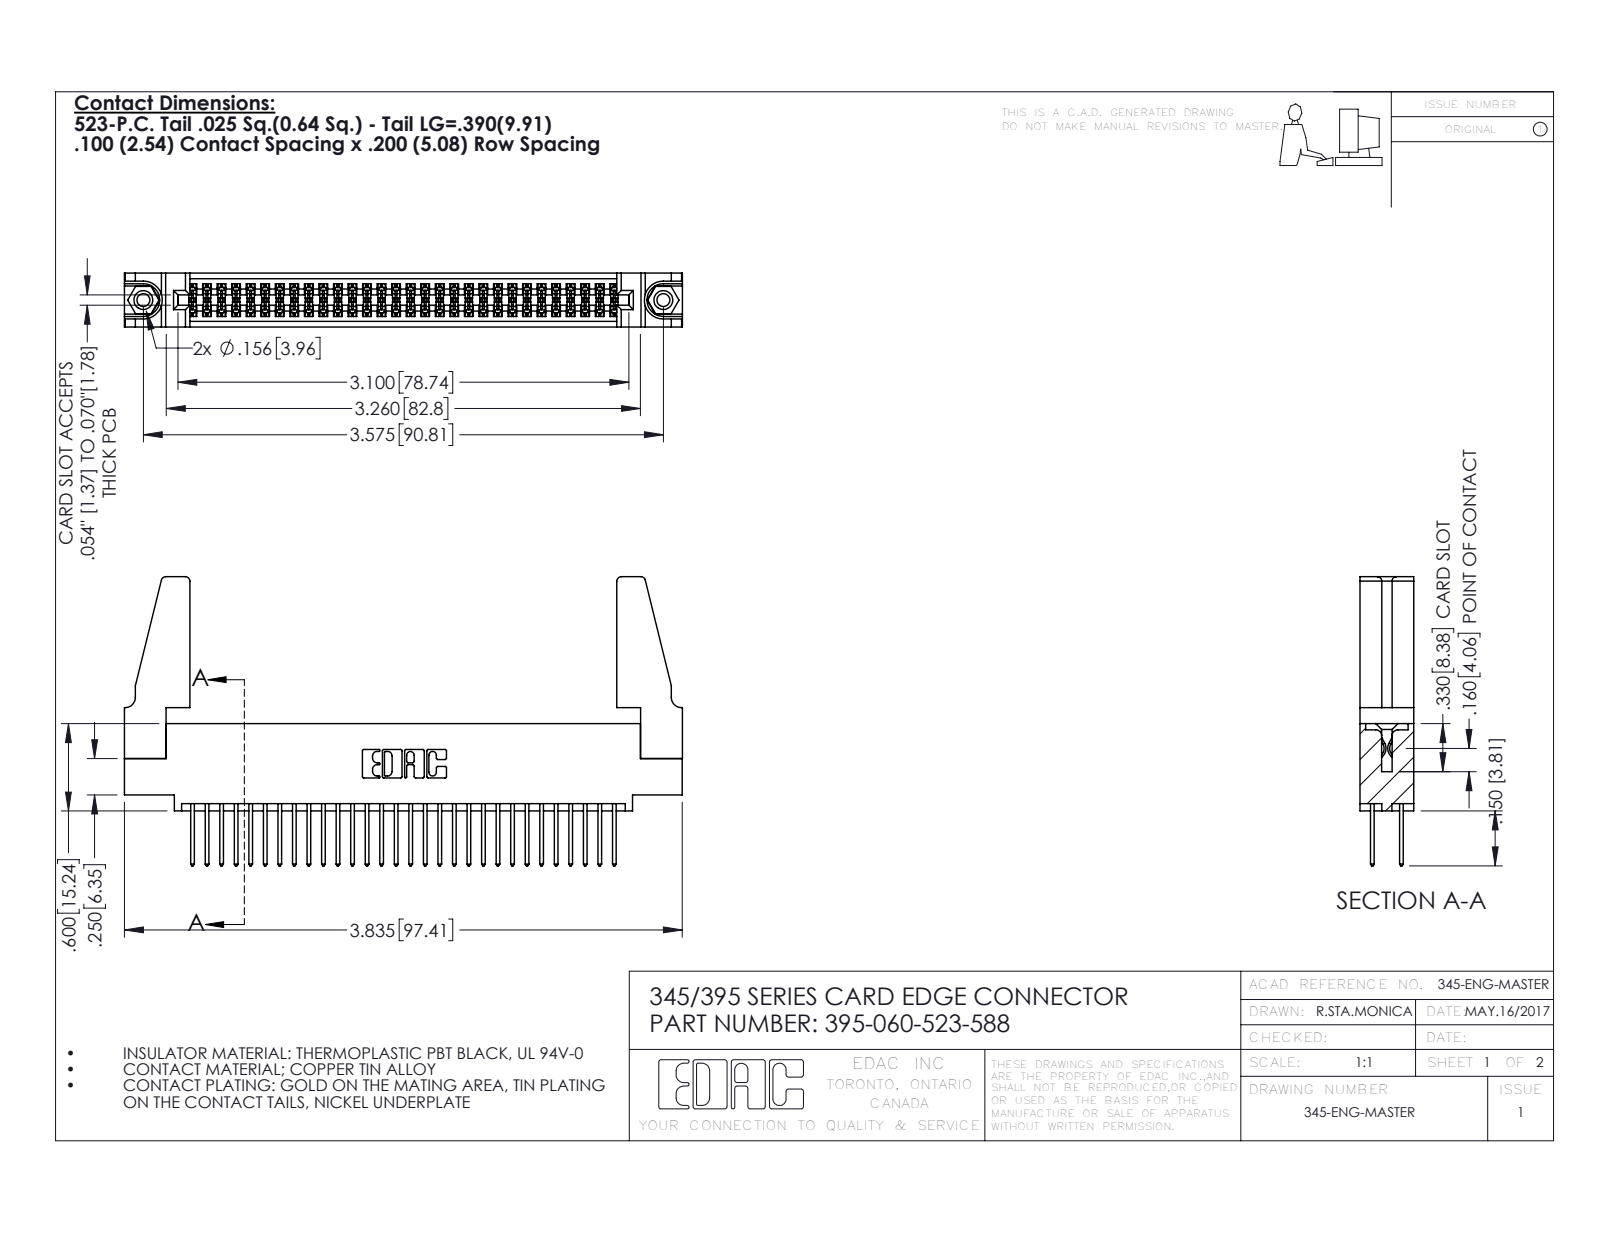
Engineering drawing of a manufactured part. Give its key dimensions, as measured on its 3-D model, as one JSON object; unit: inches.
{"part_name": "345-250-001_345-250-001-102; 345-292-001_345-293-123; 345 Part_0.110 Offset - 0.156 Dia-TH; 395-060-523-588 (+1 more)", "step_written_by": "SolidWorks 2016 (CONFIG_CONTROL_DESIGN)", "units": "inches", "bodies": {"solids": 65, "faces": 3254, "planar": 2136, "cylindrical": 1102, "other": 16}, "overall_size": [3.836, 1.987, 0.37], "volume_in3": 0.772, "surface_area_in2": 27.02, "round_holes": [[0.089, 2], [0.125, 2], [0.156, 2], [0.064, 1]], "round_bosses_or_shafts": [[0.155, 2]], "partial_cylinders_radius": [[0.006, 90], [0.01, 60], [0.01, 22], [0.03, 8], [0.007, 6], [0.031, 6], [0.026, 3], [0.014, 2]], "face_to_face_distances": [0.072, 0.298, 0.37, 0.2, 0.098, 0.272, 0.025, 0.225, 0.175, 0.149], "hole_center_spacings": [0.27, 3.34, 3.575]}
